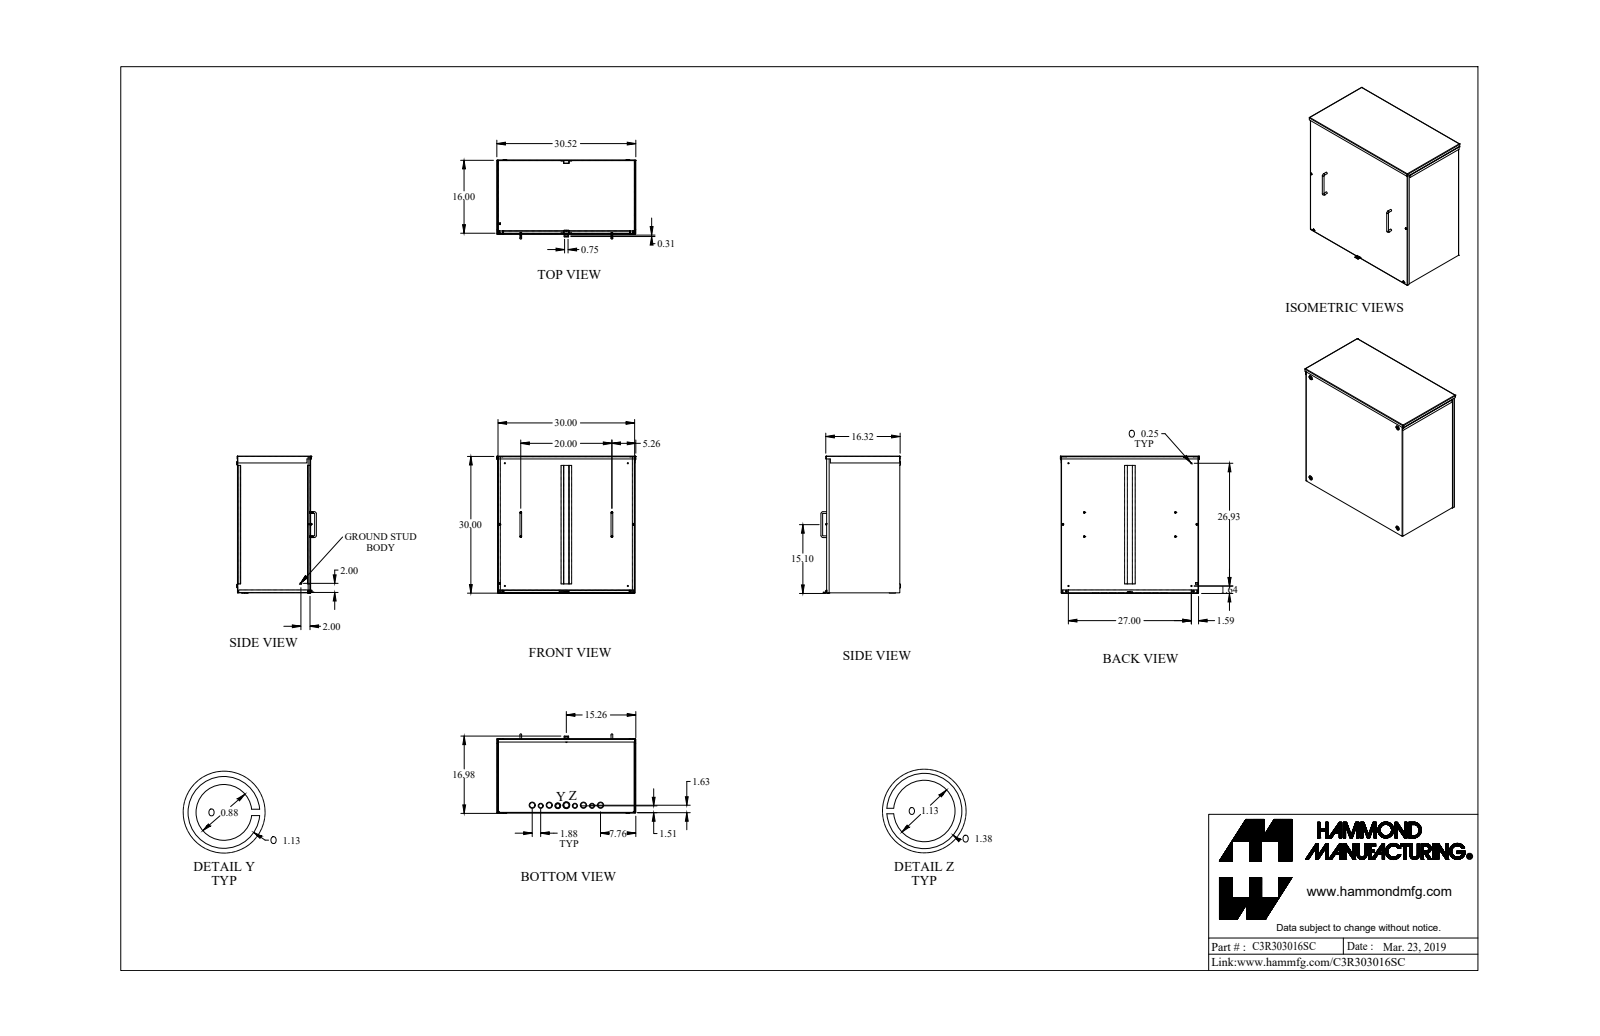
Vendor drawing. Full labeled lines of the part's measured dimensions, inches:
Part name (STEP PRODUCT): C3R303016SC_Default
STEP written by: SolidWorks 2019 (CONFIG_CONTROL_DESIGN)
Units: inches
Bodies: 19 solids, 653 faces (342 planar, 193 cylindrical, 118 other)
Overall size (bounding box): 30.519 × 30.135 × 17.478
Volume: 297.3 in³ · Surface area: 8 277 in²
Round holes (diameter × count): ⌀0.156 ×5, ⌀0.17 ×4, ⌀0.203 ×4, ⌀0.25 ×4, ⌀0.875 ×4, ⌀1.125 ×3, ⌀1.125 ×2, ⌀0.125 ×1, ⌀0.137 ×1
Round bosses / shafts (diameter × count): ⌀0.367 ×8, ⌀0.19 ×8, ⌀0.375 ×7, ⌀1.375 ×5, ⌀1.125 ×4, ⌀0.125 ×1
Partial cylindrical surfaces — rounded edges, fillets, slot ends (radius × count): R0.036 ×28, R0.108 ×28, R0.109 ×8, R0.125 ×8, R0.156 ×2, R0.029 ×1, R0.086 ×1
Main face-to-face distances: 0.072, 16, 29.928, 15.928, 30, 16.072, 0.072, 29.856, 29.856, 29.928
Hole centre spacings: 20, 3.75, 7.5, 0.024, 1.879, 1.88, 5.3, 5.392
